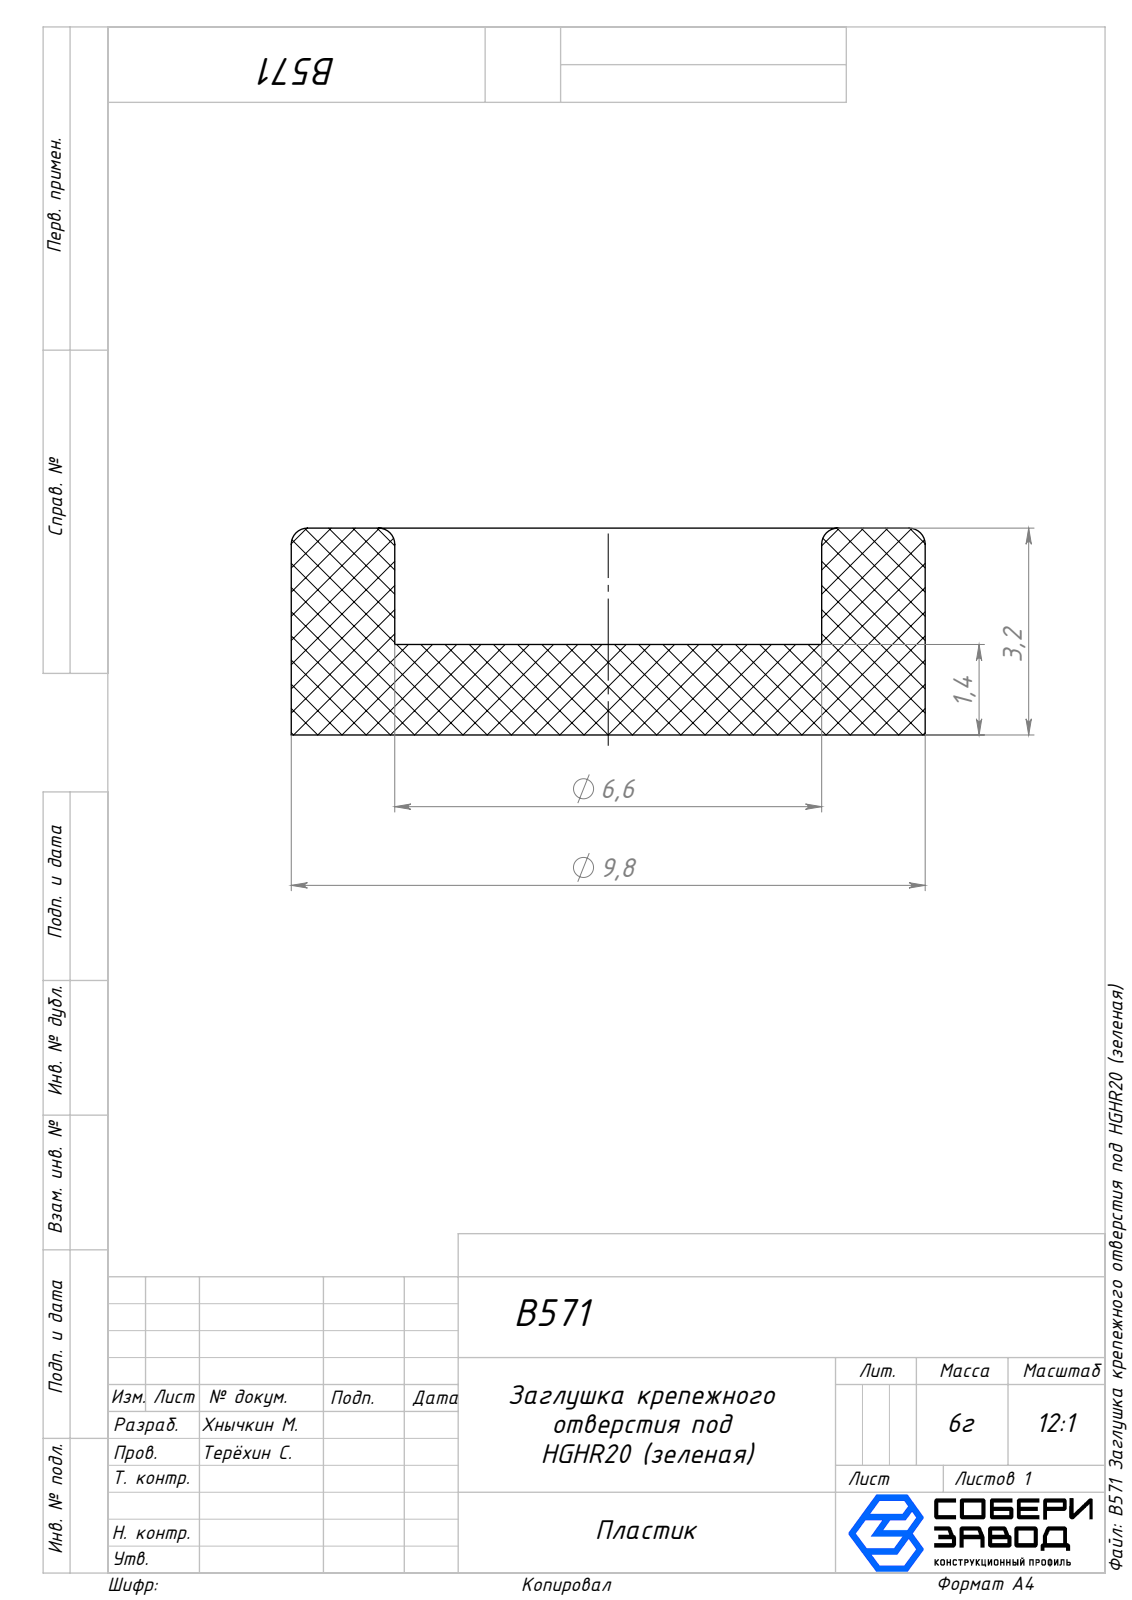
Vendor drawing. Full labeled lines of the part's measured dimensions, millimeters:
Part name (STEP PRODUCT): B571 Заглушка крепежного отверстия под HGHR20 (зеленая)
STEP written by: SolidWorks 2025 (AUTOMOTIVE_DESIGN)
Units: millimetres
Bodies: 1 solid, 11 faces (3 planar, 4 cylindrical, 4 other)
Overall size (bounding box): 9.8 × 9.8 × 3.2
Volume: 179 mm³ · Surface area: 281 mm²
Round holes (diameter × count): ⌀6.6 ×1
Round bosses / shafts (diameter × count): ⌀9.8 ×1
Main face-to-face distances: 1.4, 3.2, 1.8
